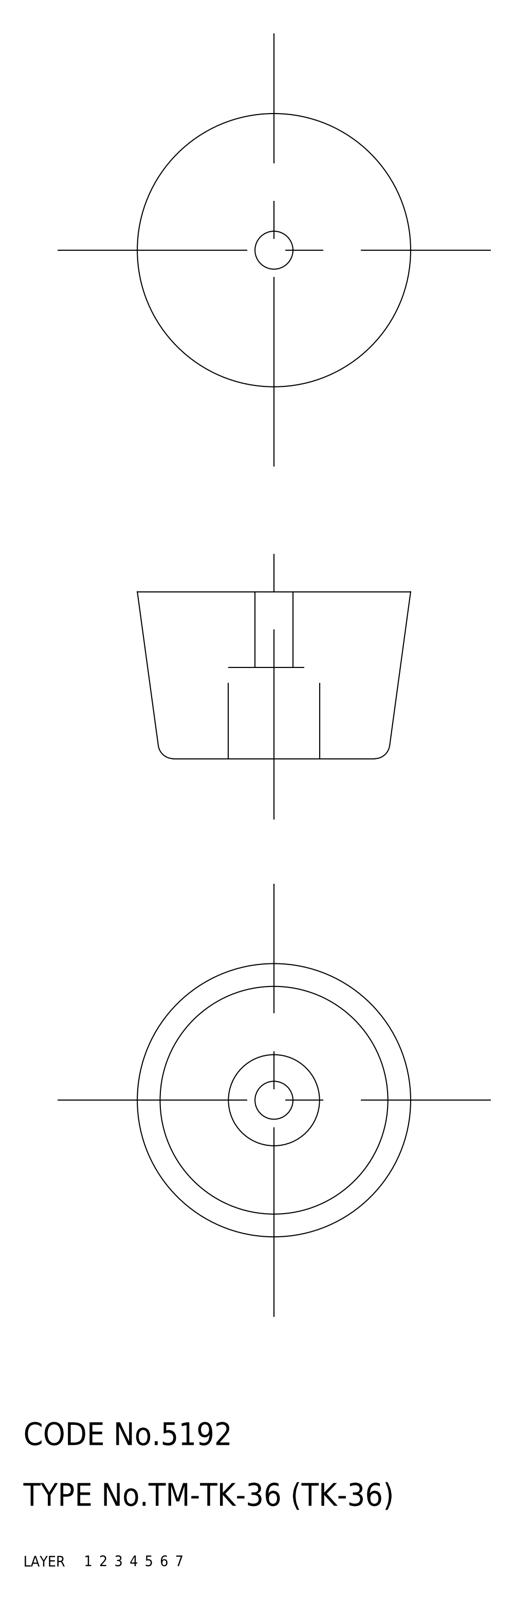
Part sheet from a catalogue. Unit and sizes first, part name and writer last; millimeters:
Units: millimetres
Overall size (bounding box): 36 × 36 × 22
Volume: 17 299 mm³ · Surface area: 5 158 mm²
Bodies: 2 solids, 20 faces (0 planar, 0 cylindrical, 20 other)
Part name (STEP PRODUCT): washer; rubber foot; TK_36_9816_36
STEP written by: CADfix (AUTOMOTIVE_DESIGN)
